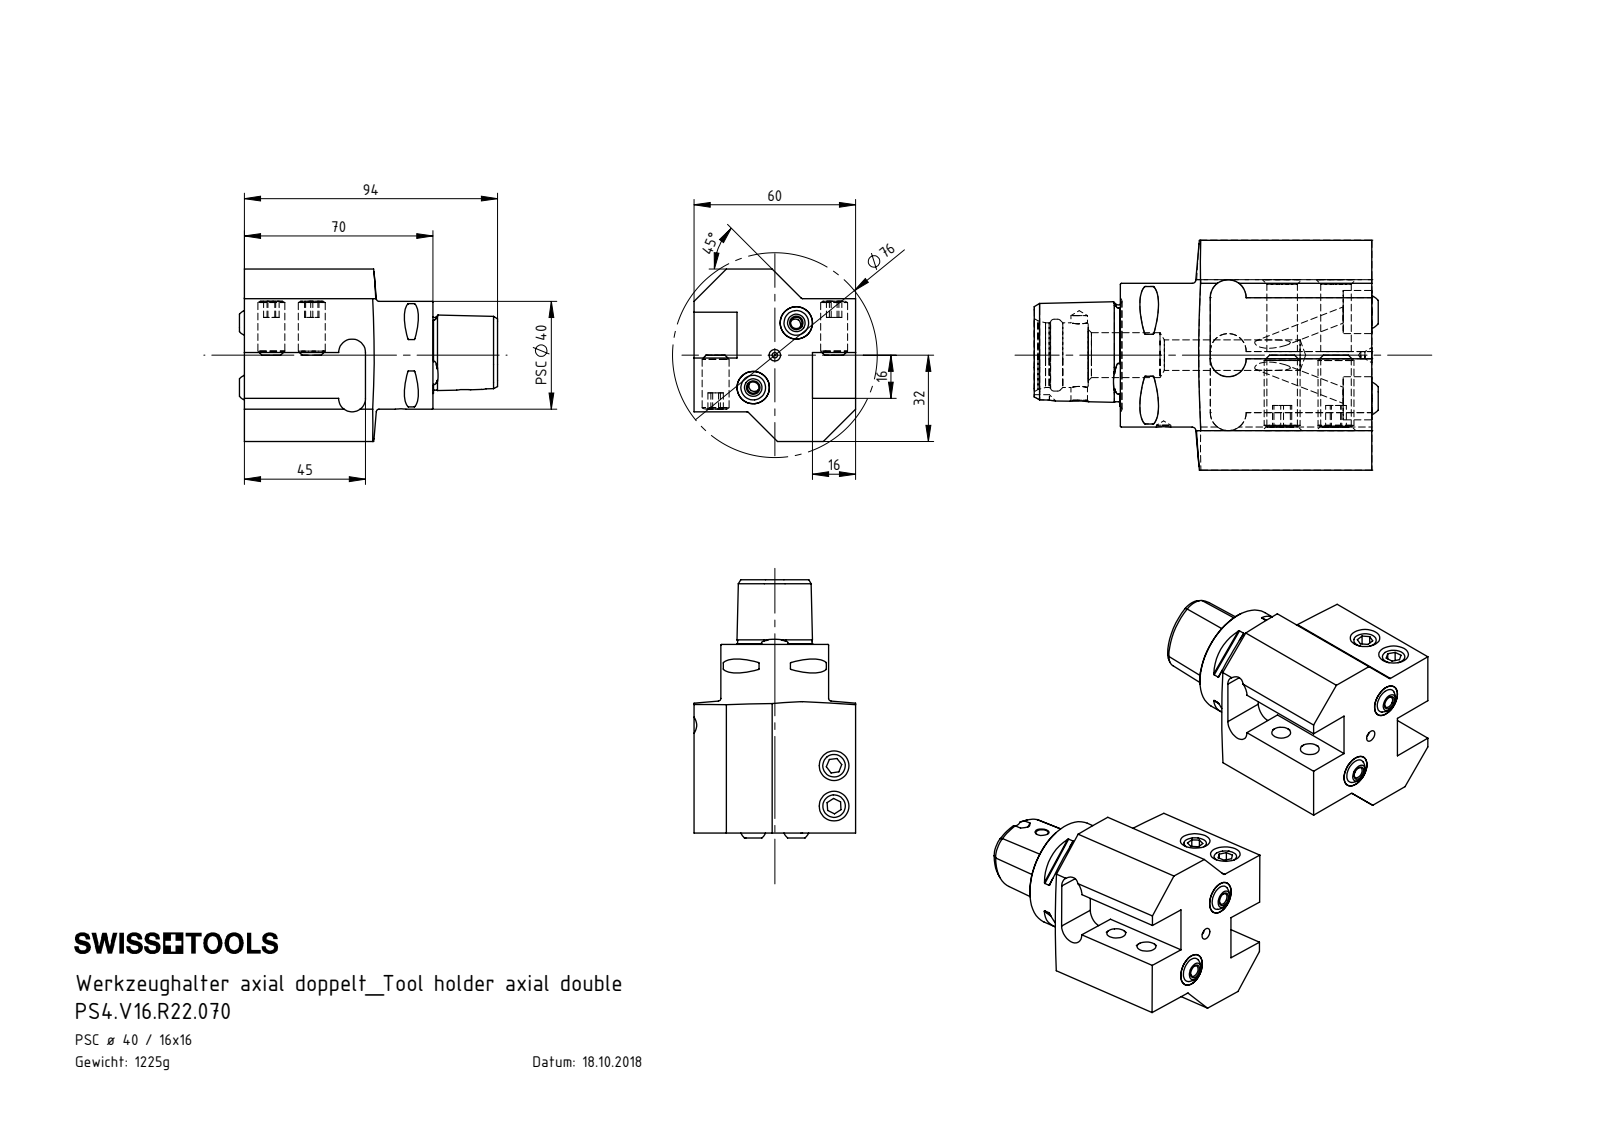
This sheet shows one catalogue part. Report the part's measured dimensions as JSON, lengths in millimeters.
{"part_name": "PS4.V16.R22.070; KU1-U12.001.010; KU1-U12.001.010_2; KU1-U12.001.010_1 (+2 more)", "step_written_by": "SolidWorks 2017 (CONFIG_CONTROL_DESIGN)", "units": "millimeters", "bodies": {"solids": 9, "faces": 286, "planar": 83, "cylindrical": 73, "other": 130}, "overall_size": [95.8, 64, 60], "volume_mm3": 156676, "surface_area_mm2": 35697, "round_holes": [[8.5, 5], [4.2, 4], [7, 2], [12, 2], [2, 1], [4, 1], [4.6, 1], [12.5, 1], [18, 1], [20, 1]], "round_bosses_or_shafts": [[10, 4], [40, 1]], "partial_cylinders_radius": [[0.3, 8], [5, 4], [0.8, 2], [3, 1]], "face_to_face_distances": [16, 44, 53, 11, 37, 5, 60, 48, 15, 20], "hole_center_spacings": [14.42, 15, 39.66, 44, 46.49, 52.8, 60.63, 74.81]}
